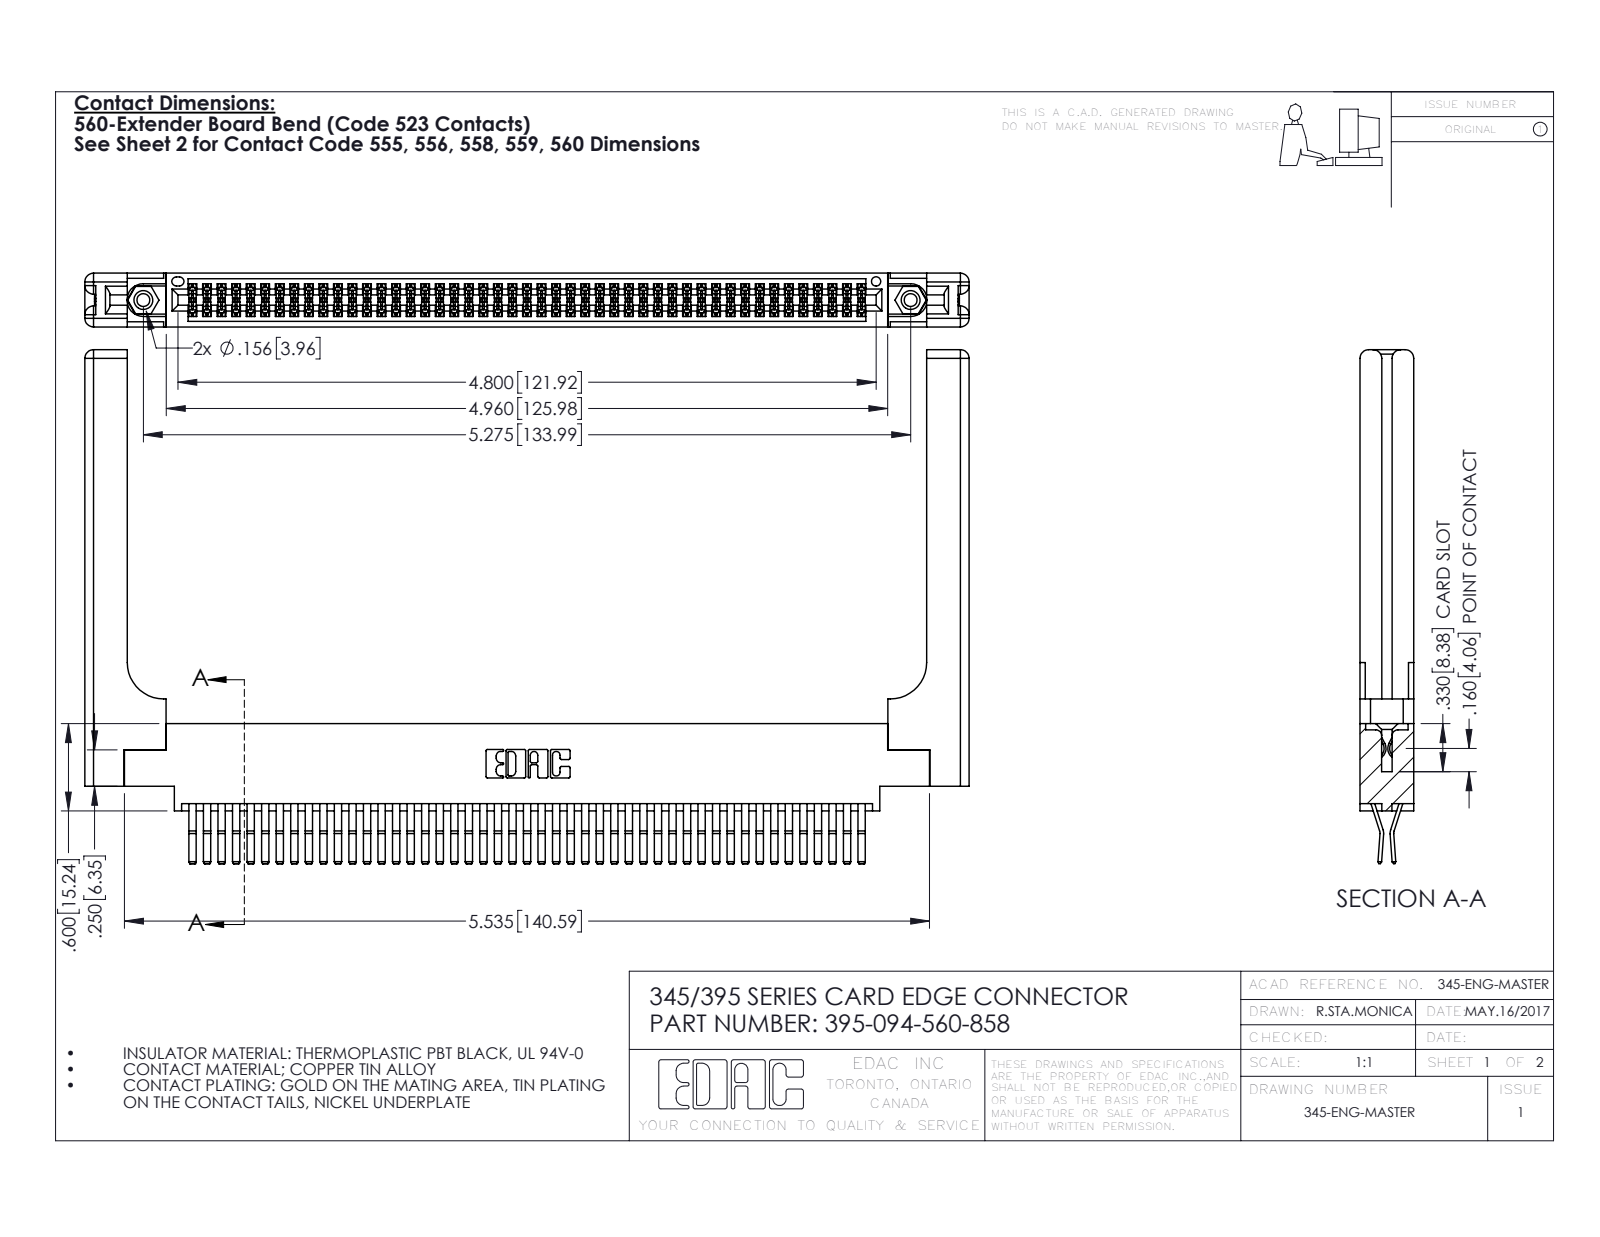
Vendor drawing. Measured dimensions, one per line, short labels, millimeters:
name: 345-250-001_345-250-001-102; 345 Part_0.170 Offset - 0.156 Dia-TH; 395-094-560-858; 345-220-058_345-220-058 (+1 more)
written by: SolidWorks 2016 (CONFIG_CONTROL_DESIGN)
unit: mm
bodies: 99 solids, 5274 faces (3334 planar, 1880 cylindrical, 60 other)
size: 154.4 × 89.7 × 9.4
volume: 24 020 mm³; area: 29 860 mm²
holes: 2× ⌀2.3, 2× ⌀3.2, 2× ⌀4, 1× ⌀1.6
bosses: 2× ⌀3.9
rounds: 141× R0.2, 22× R0.3, 16× R1.5, 6× R0.2, 6× R0.8, 3× R0.7, 2× R0.3, 2× R0.4
face distances: 1.8, 9.4, 7.6, 0.6, 2.5, 6.9, 5.1, 5.7, 3.8, 3.8
hole spacings: 6.9, 128, 134
